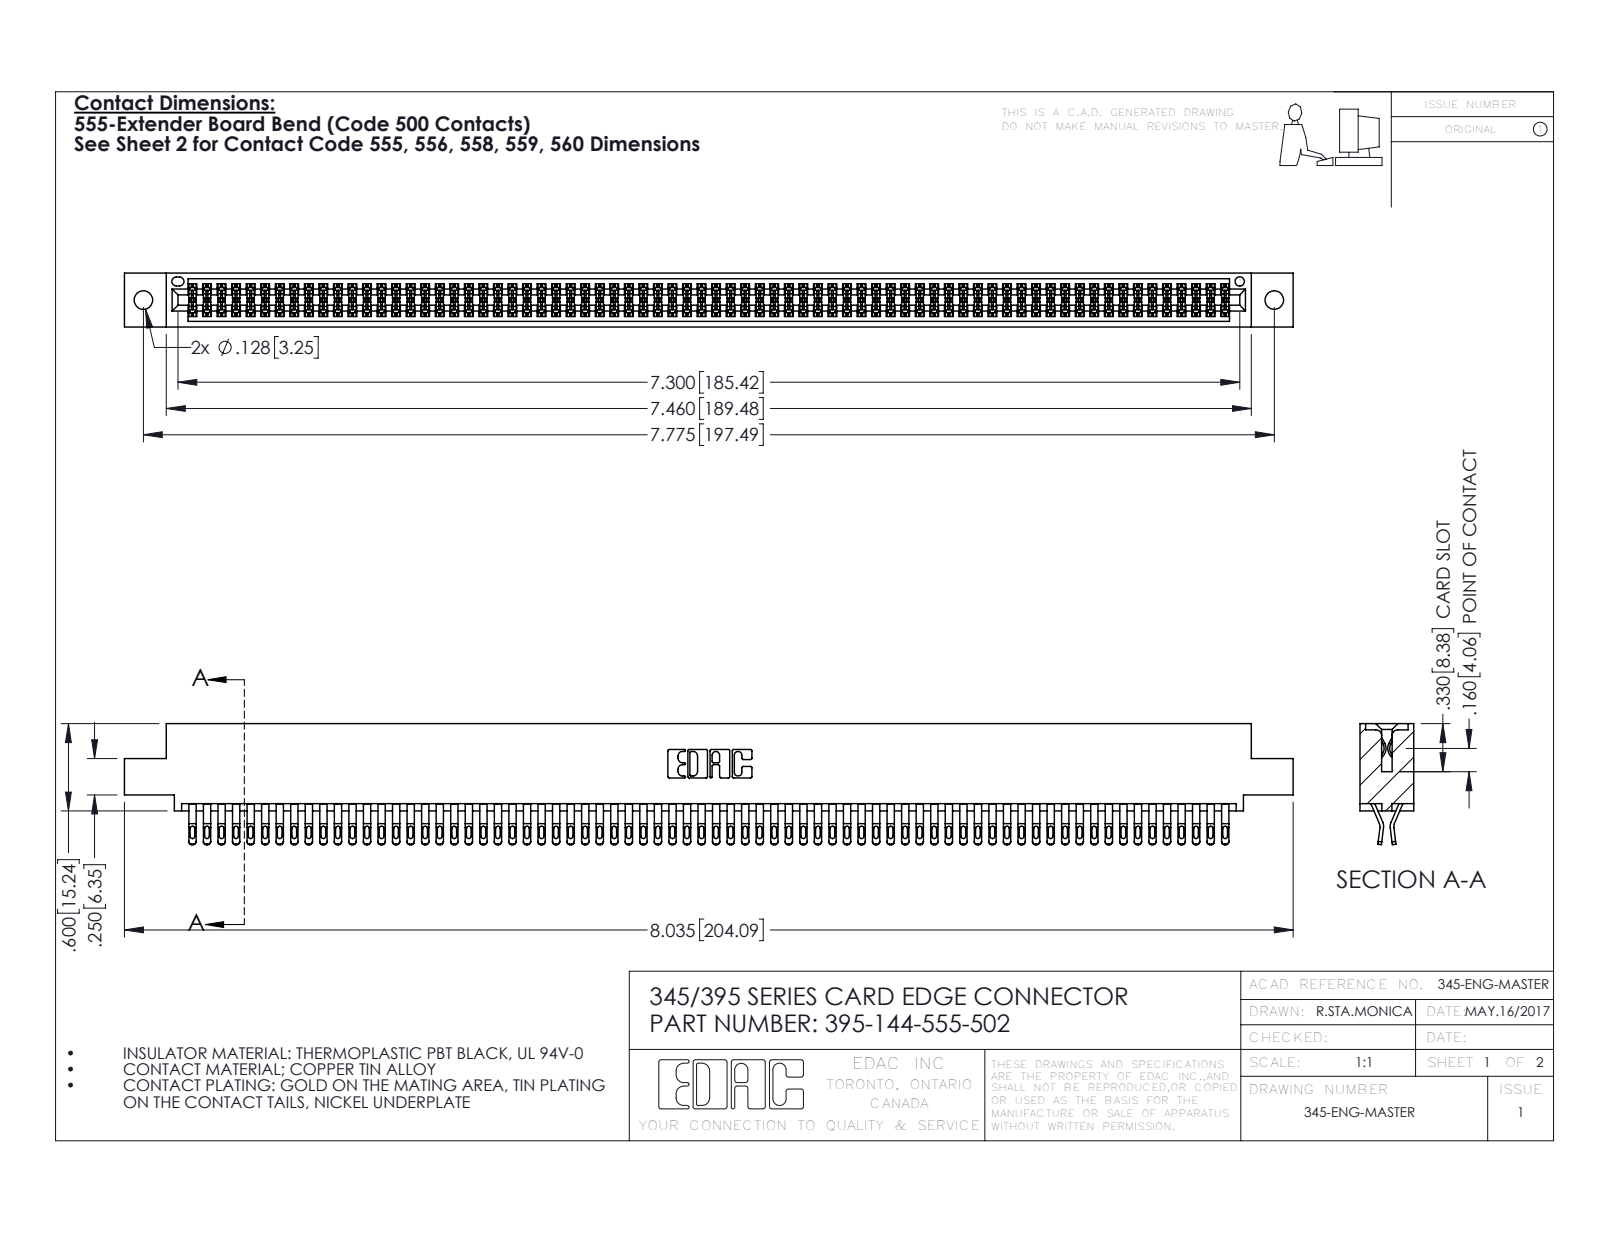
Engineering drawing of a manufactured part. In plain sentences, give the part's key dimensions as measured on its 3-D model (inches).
The part is named "345-292-001_555 Tail; 395-144-555-502; 345 Part_0.110 Offset - 0.128 Dia". Its 3-D file was written by "SolidWorks 2016 (CONFIG_CONTROL_DESIGN)". It is 145 solids with 8194 faces: 4548 planar, 3646 cylindrical and 0 other. Overall it measures 8.035 by 0.832 by 0.37 inches. Its volume is 1.246 cubic inches and its surface area 49.64 square inches. Round holes: 2 of diameter 0.128, 1 of diameter 0.064. Partial cylindrical surfaces (rounded edges, fillets, slot ends): 360 of radius 0.016, 288 of radius 0.02, 216 of radius 0.006, 22 of radius 0.01, 6 of radius 0.007, 6 of radius 0.031, 3 of radius 0.026, 2 of radius 0.01. The main face-to-face distances are 0.298, 0.072, 0.025, 0.37, 0.2, 0.098, 0.272, 0.225, 0.175, 0.149. The hole center spacings are 0.27, 7.539, 7.775.
